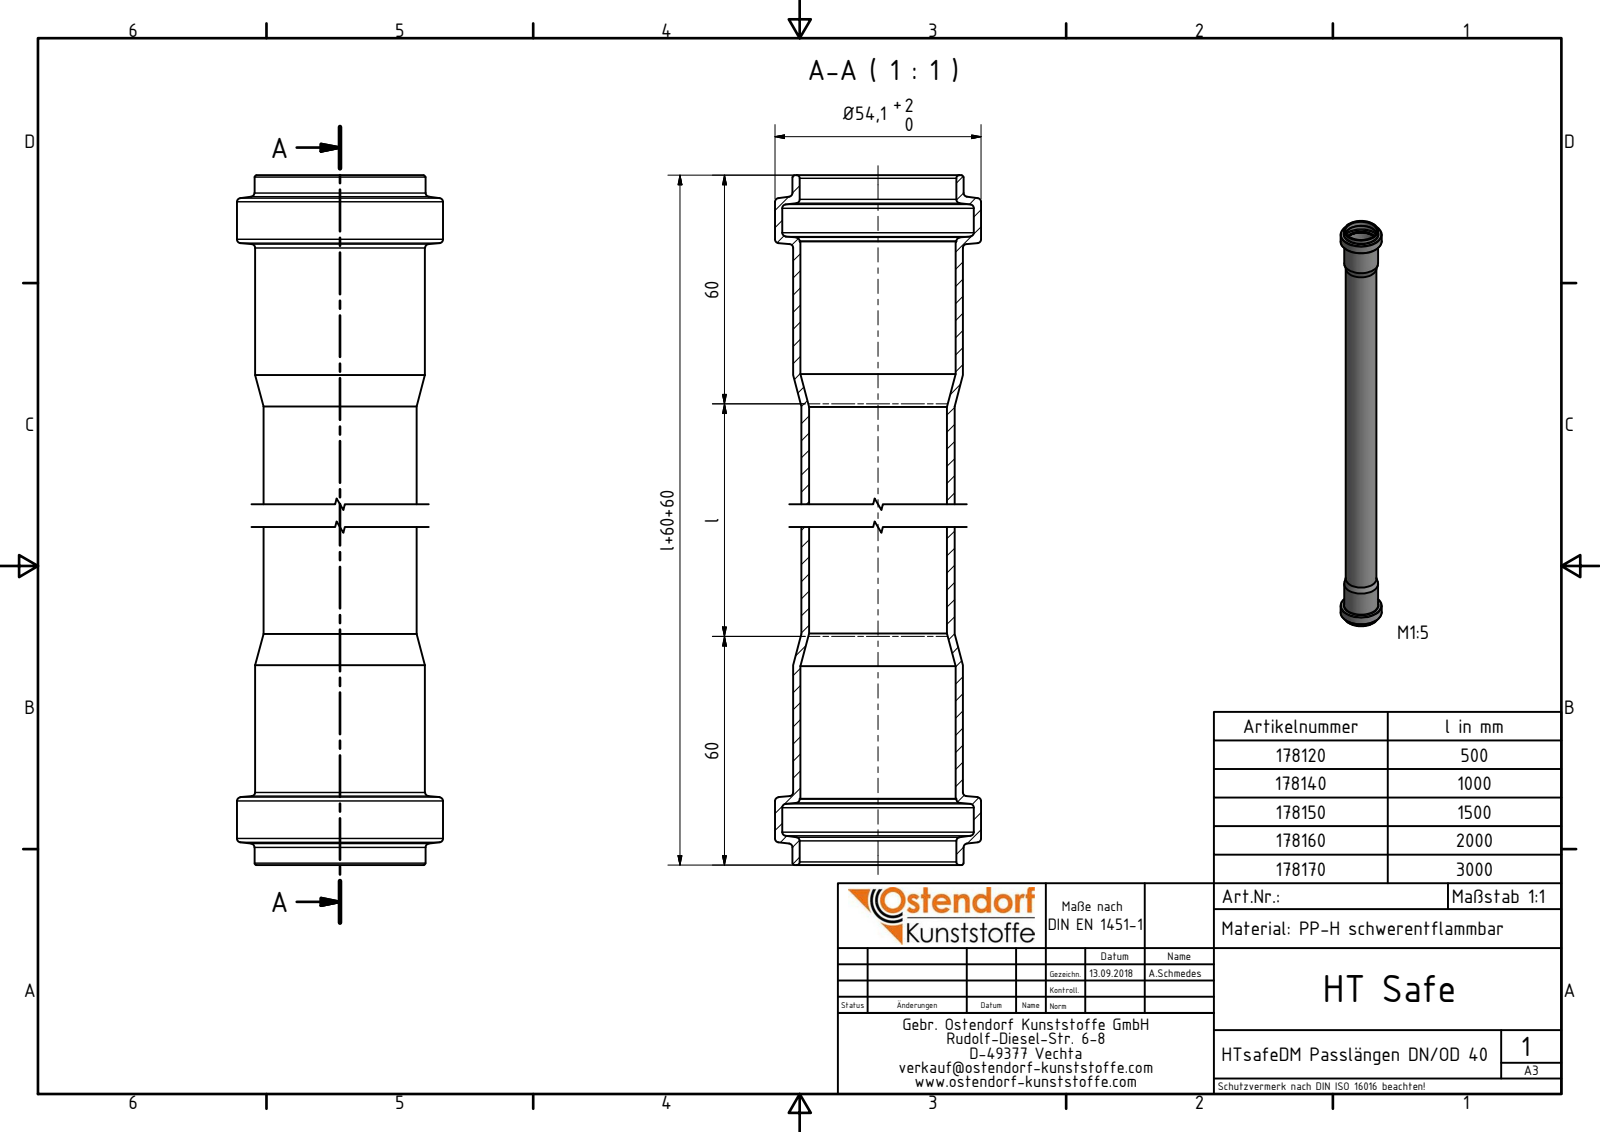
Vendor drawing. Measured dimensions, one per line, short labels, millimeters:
name: 178150 HTsafeDM DN_OD 40x1500
written by: Autodesk Inventor 2016 (AUTOMOTIVE_DESIGN)
unit: mm
bodies: 1 solid, 52 faces (4 planar, 16 cylindrical, 32 other)
size: 1620 × 54.1 × 54.1
volume: 396 445 mm³; area: 398 043 mm²
holes: 1× ⌀36.2, 1× ⌀40.8, 1× ⌀41.1, 1× ⌀50.3
bosses: 1× ⌀54.1, 1× ⌀44.9, 1× ⌀44.6, 1× ⌀40.2
face distances: 1620, 17.4, 1602.6, 1585.2
